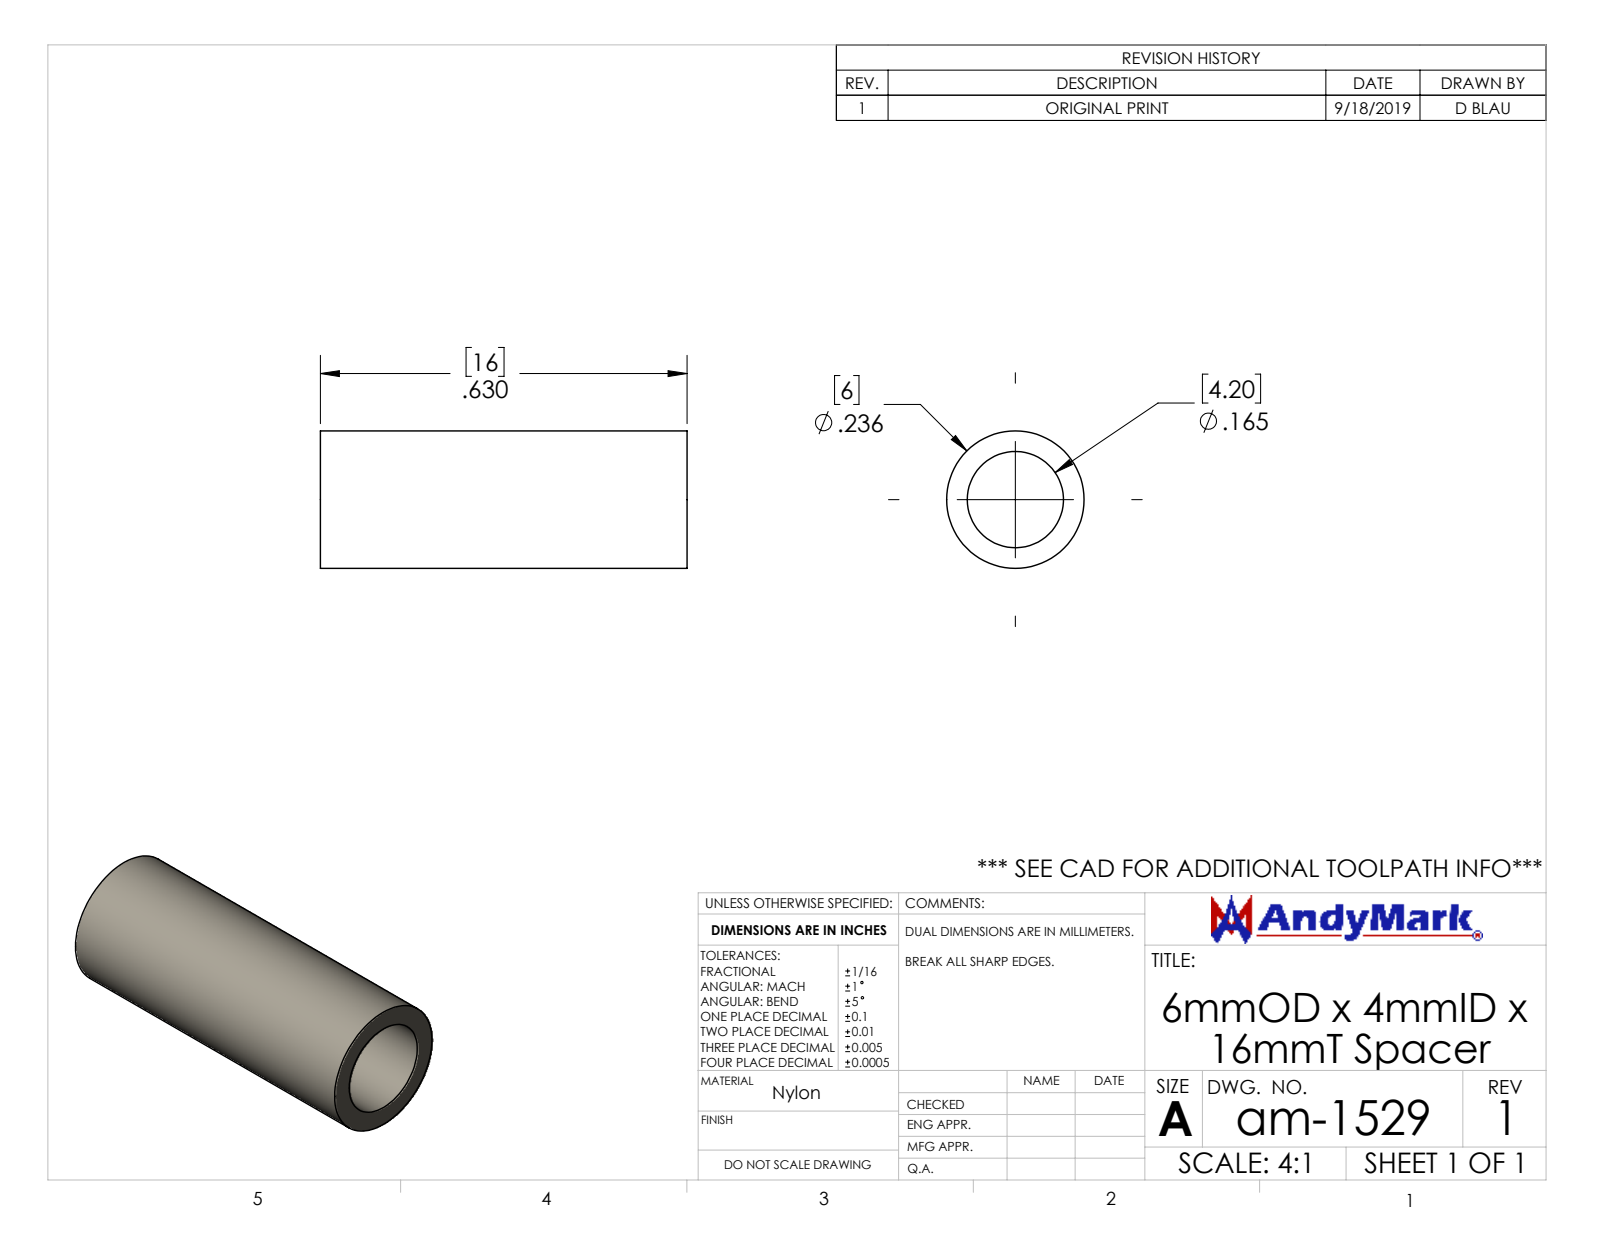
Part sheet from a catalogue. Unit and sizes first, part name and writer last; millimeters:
Units: millimetres
Overall size (bounding box): 16 × 6 × 6
Round holes (diameter × count): ⌀4.2 ×1
Round bosses / shafts (diameter × count): ⌀6 ×1
Main face-to-face distances: 16
Volume: 231 mm³ · Surface area: 542 mm²
Bodies: 1 solid, 6 faces (2 planar, 4 cylindrical, 0 other)
Part name (STEP PRODUCT): am-1529 6mmOD x 4mmID x 16mmt Spacer
STEP written by: SolidWorks 2019 (AUTOMOTIVE_DESIGN)
